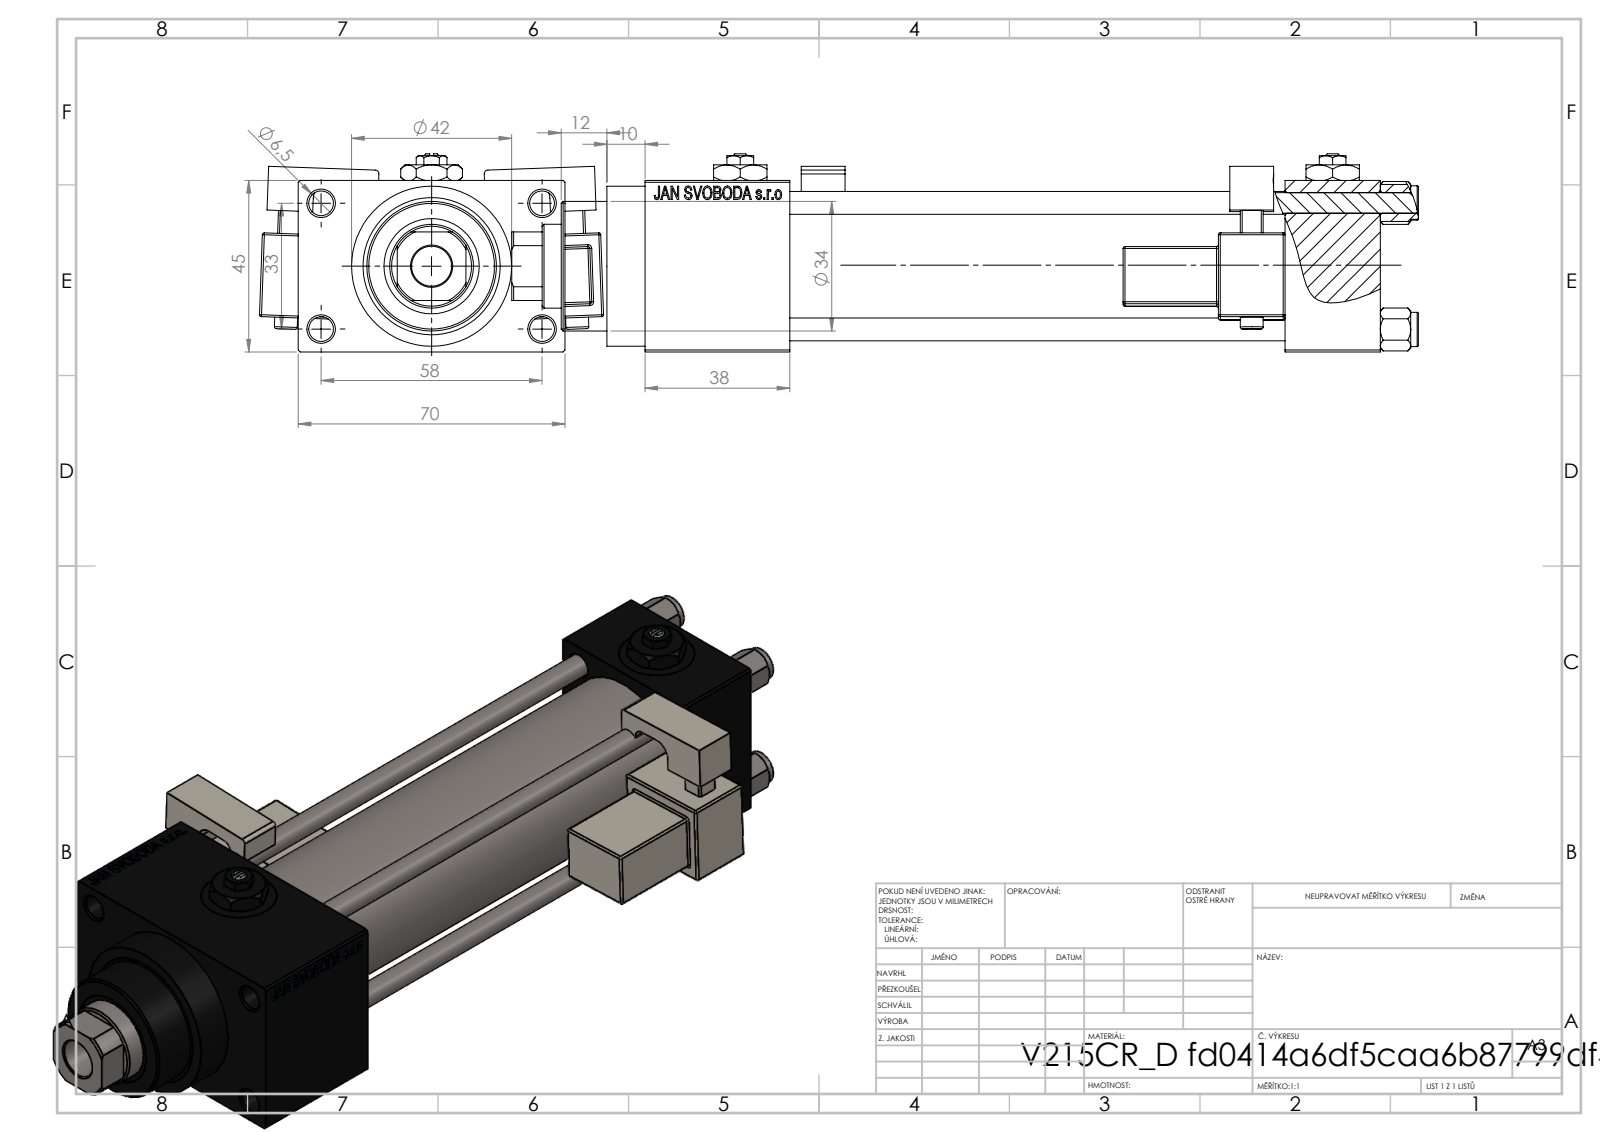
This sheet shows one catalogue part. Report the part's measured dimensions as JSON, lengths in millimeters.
{"part_name": "V215CR_D_Body; V215CR_MSU; NUT_M5_D; V215_VC_A (+3 more)", "step_written_by": "SolidWorks 2019 (CONFIG_CONTROL_DESIGN)", "units": "millimeters", "bodies": {"solids": 15, "faces": 1361, "planar": 604, "cylindrical": 159, "other": 598}, "overall_size": [238, 90.31, 52], "volume_mm3": 348130, "surface_area_mm2": 122778, "round_holes": [[6, 4], [6.5, 4], [13.16, 4], [20, 4], [7, 3], [10.5, 1], [22, 1], [24, 1], [25, 1], [32, 1], [33, 1]], "round_bosses_or_shafts": [[9, 4], [6, 2], [42, 1], [38, 1], [34, 1]], "partial_cylinders_radius": [[0.5, 48], [1, 2], [2.5, 2], [4, 2], [10.5, 1]], "face_to_face_distances": [45, 25, 130, 12.5, 3, 57.5, 155, 38, 168, 70], "hole_center_spacings": [12.4, 23.48, 33.2, 33.37, 35.35, 45.6, 56.35, 33]}
